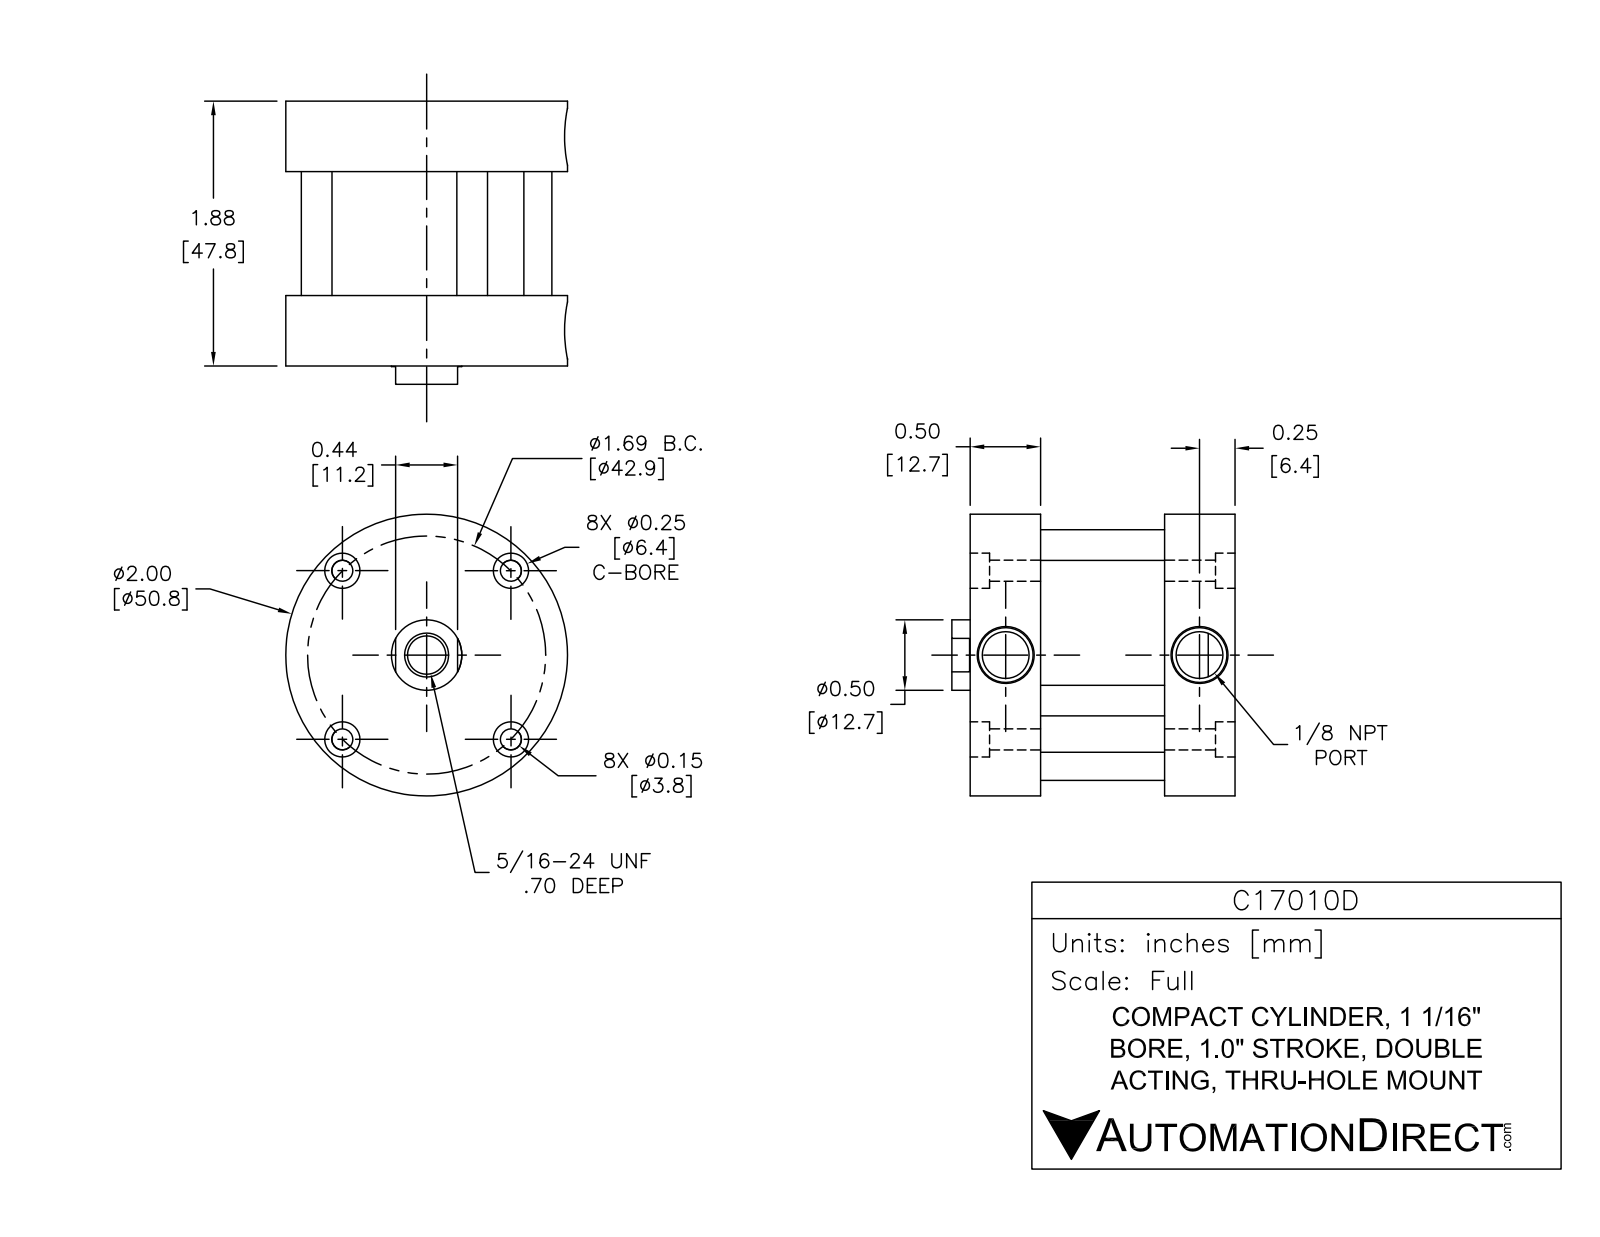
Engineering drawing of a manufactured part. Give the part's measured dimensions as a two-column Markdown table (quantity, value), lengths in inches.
| quantity | value |
| --- | --- |
| part name | C17010D-rod_part; C17010D-FO1_BM_rod; C17010D-FO1_BM_tube; C17010D-FO1_BM_heads (2) (+3 more) |
| STEP written by | SolidWorks 2014 (AUTOMOTIVE_DESIGN) |
| units | inches |
| bodies | 9 solids, 165 faces (49 planar, 98 cylindrical, 18 other) |
| overall size | 2.01 × 2 × 2 |
| volume | 3.319 in³ |
| surface area | 44.04 in² |
| round holes (diameter × count) | 0.136 × 4, 0.156 × 4, 0.25 × 4, 0.125 × 2, 0.267 × 1, 0.5 × 1, 0.502 × 1, 1.062 × 1, 1.122 × 1 |
| round bosses / shafts (diameter × count) | 0.272 × 4, 2 × 1 |
| main face-to-face distances | 0.5, 1.38, 0.282, 1.598, 0.218, 1.098, 1.88, 0.88, 1.316, 0.598 |
| hole center spacings | 0.33, 0.845, 0.845, 0.939, 1.195, 1.195, 1.406, 1.657 |
